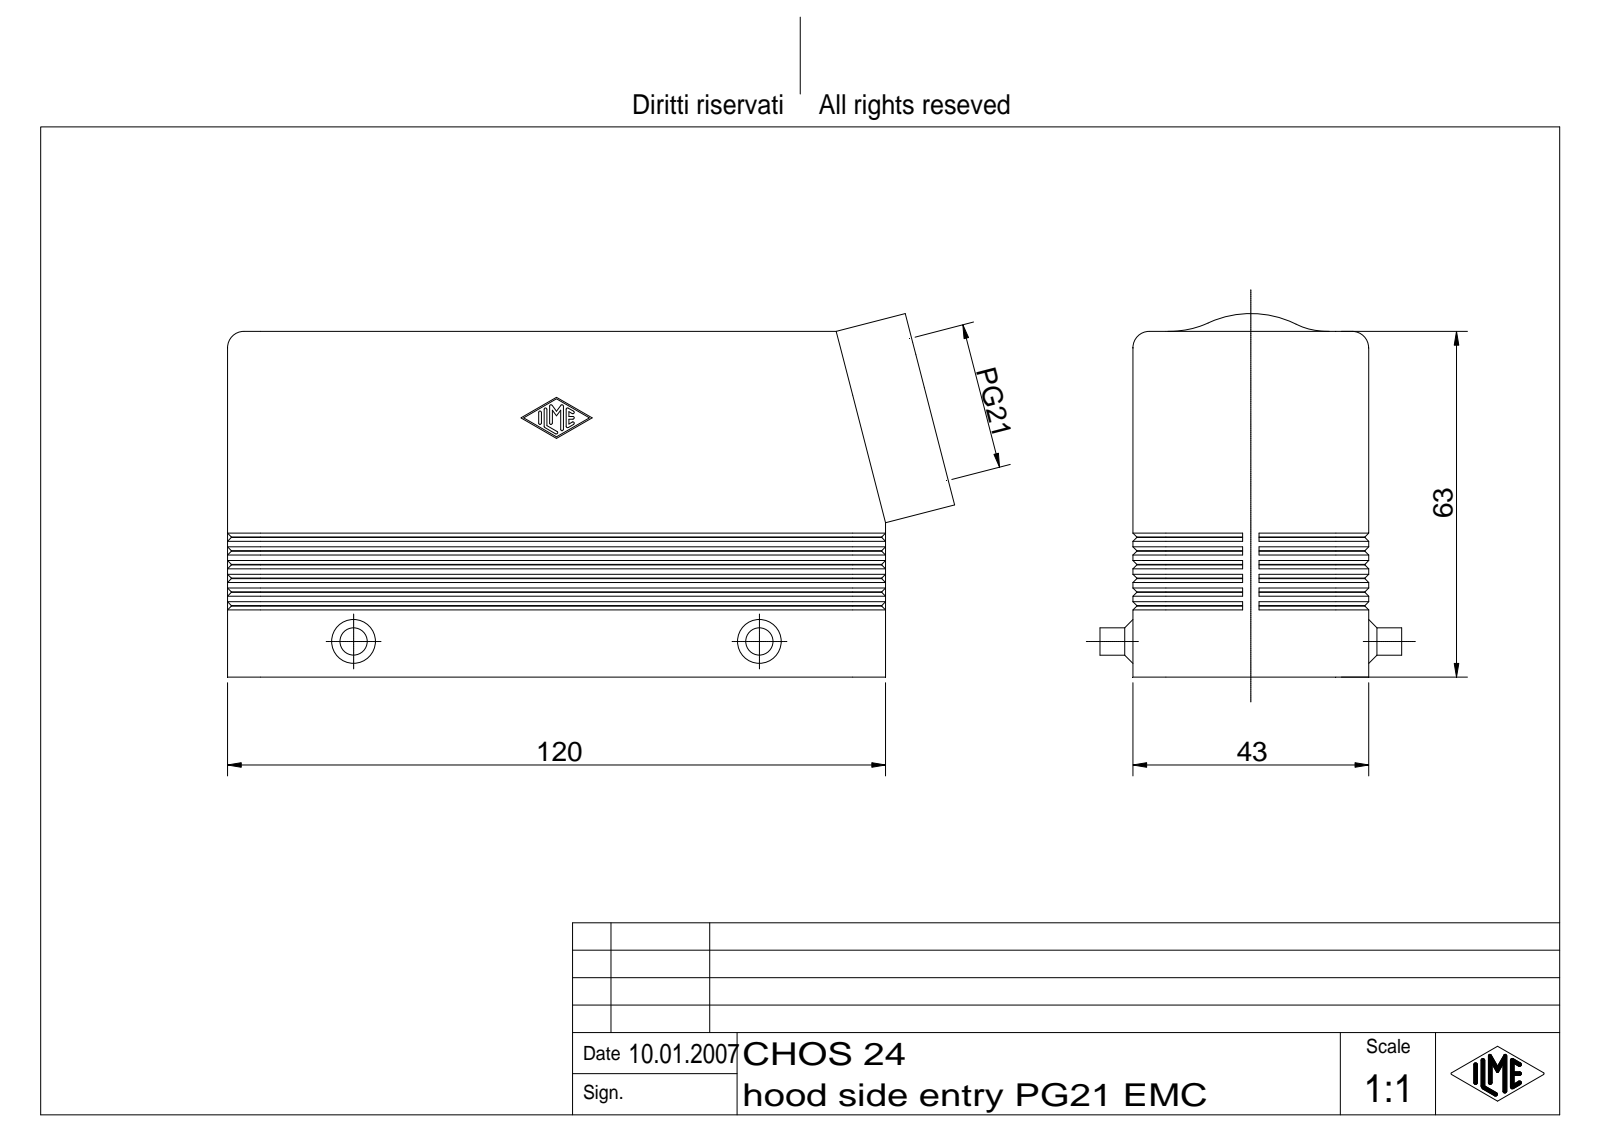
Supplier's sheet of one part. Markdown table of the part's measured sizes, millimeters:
| quantity | value |
| --- | --- |
| part name | CHO Tüllengehäuse 2 Bügel für einen Einsatz |
| STEP written by | Autodesk Inventor 7 (AUTOMOTIVE_DESIGN) |
| units | millimeters |
| bodies | 1 solid, 497 faces (184 planar, 113 cylindrical, 200 other) |
| overall size | 132.59 × 66.25 × 55 |
| volume | 87 890 mm³ |
| surface area | 50 654 mm² |
| round holes (diameter × count) | 24.78 × 1, 26.78 × 1 |
| round bosses / shafts (diameter × count) | 5 × 2 |
| partial cylindrical surfaces (radius × count) | 0.25 × 14, 3 × 7, 2 × 4, 6 × 4, 5.3 × 2, 1.5 × 1 |
| main face-to-face distances | 3, 40, 37, 43, 8.5, 11.5, 1.77, 5.3, 105.5, 29.34 |
